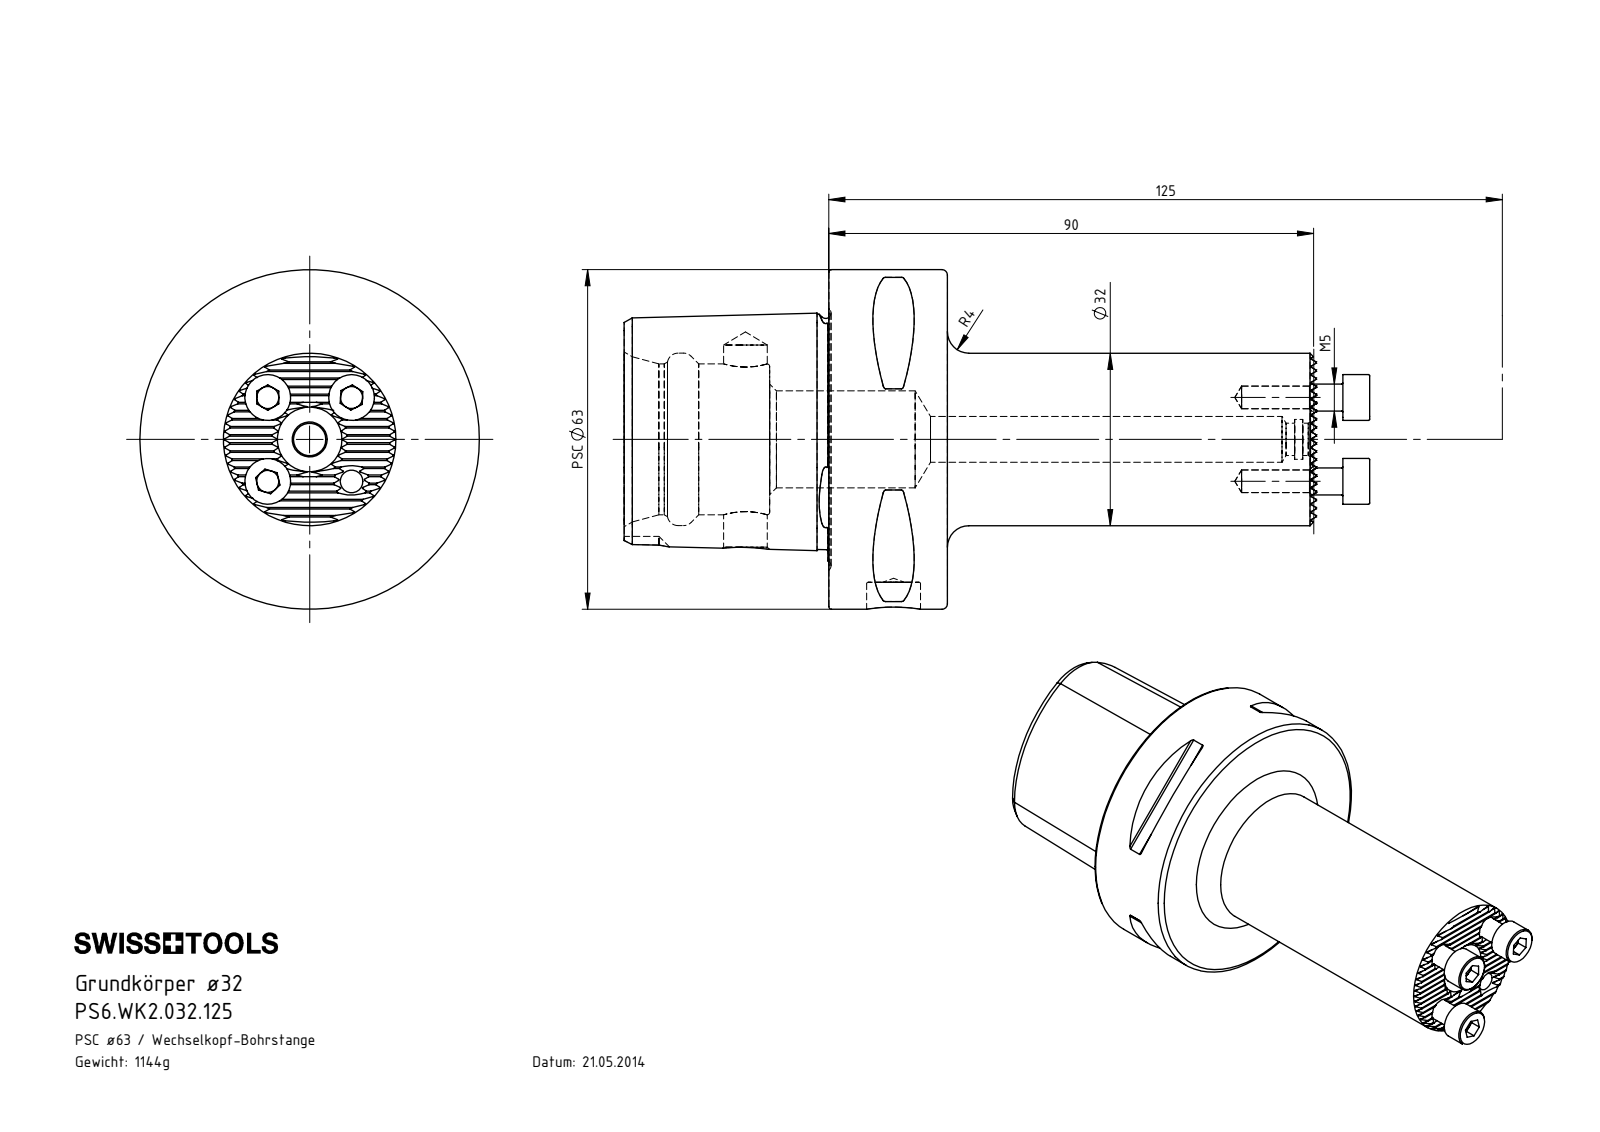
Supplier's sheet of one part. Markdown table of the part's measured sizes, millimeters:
| quantity | value |
| --- | --- |
| part name | ISO 4762 - M5 x 14; PS6-WK2.032.125_B; DIN 3771 - 6x1; PS6.WK2.032.125 |
| STEP written by | SolidWorks 2017 (AUTOMOTIVE_DESIGN) |
| units | millimeters |
| bodies | 5 solids, 421 faces (197 planar, 97 cylindrical, 127 other) |
| overall size | 138.4 × 63 × 63 |
| volume | 147 424 mm³ |
| surface area | 30 961 mm² |
| round holes (diameter × count) | 4.2 × 4, 4 × 1, 6 × 1, 7.4 × 1, 8.1 × 1, 8.5 × 1, 18 × 1, 28 × 1, 32 × 1 |
| round bosses / shafts (diameter × count) | 8.5 × 3, 5 × 3, 63 × 1 |
| partial cylindrical surfaces (radius × count) | 0.12 × 21, 0.5 × 8, 6 × 1 |
| main face-to-face distances | 22, 1.3, 2.6, 38, 60, 3.9, 5.2, 11, 12.99, 6.5 |
| hole center spacings | 11, 15.56, 22.01, 27.5 |
